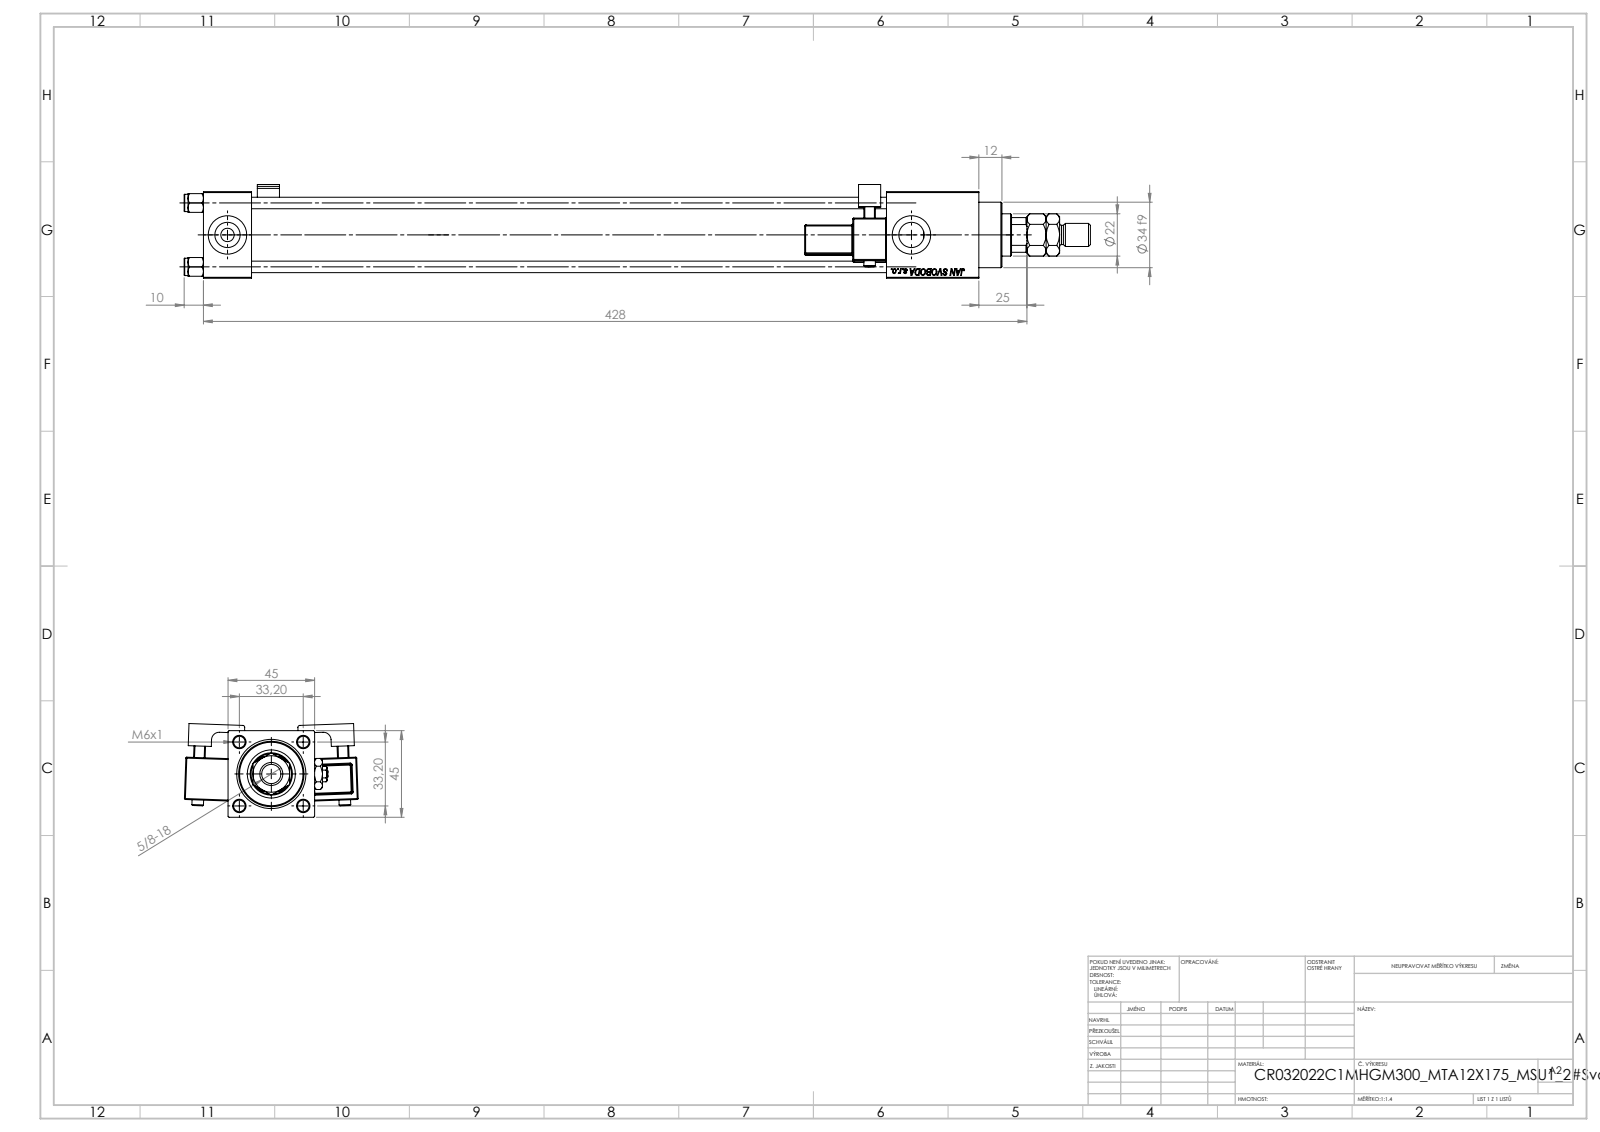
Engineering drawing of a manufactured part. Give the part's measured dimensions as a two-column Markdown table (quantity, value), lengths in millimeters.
| quantity | value |
| --- | --- |
| part name | V215CR_C_TYCINKA; V215CR_MSU; V215CR_VCP_C; MTA (+4 more) |
| STEP written by | SolidWorks 2019 (CONFIG_CONTROL_DESIGN) |
| units | millimeters |
| bodies | 15 solids, 1402 faces (626 planar, 154 cylindrical, 622 other) |
| overall size | 471 × 90.31 × 48.72 |
| volume | 487 255 mm³ |
| surface area | 188 421 mm² |
| round holes (diameter × count) | 6 × 4, 7 × 2, 13.16 × 2, 20 × 2, 10.5 × 1, 22 × 1, 24 × 1, 25 × 1, 32 × 1, 33 × 1 |
| round bosses / shafts (diameter × count) | 9 × 4, 6 × 2, 38 × 1, 34 × 1, 12 × 1, 10 × 1 |
| partial cylindrical surfaces (radius × count) | 0.5 × 48, 1 × 2, 2.5 × 2, 4 × 2, 10.5 × 1 |
| main face-to-face distances | 45, 25, 3, 355, 330, 403, 22.99, 312.5, 378, 13 |
| hole center spacings | 23.48, 33.2, 46.95, 355.5 |
